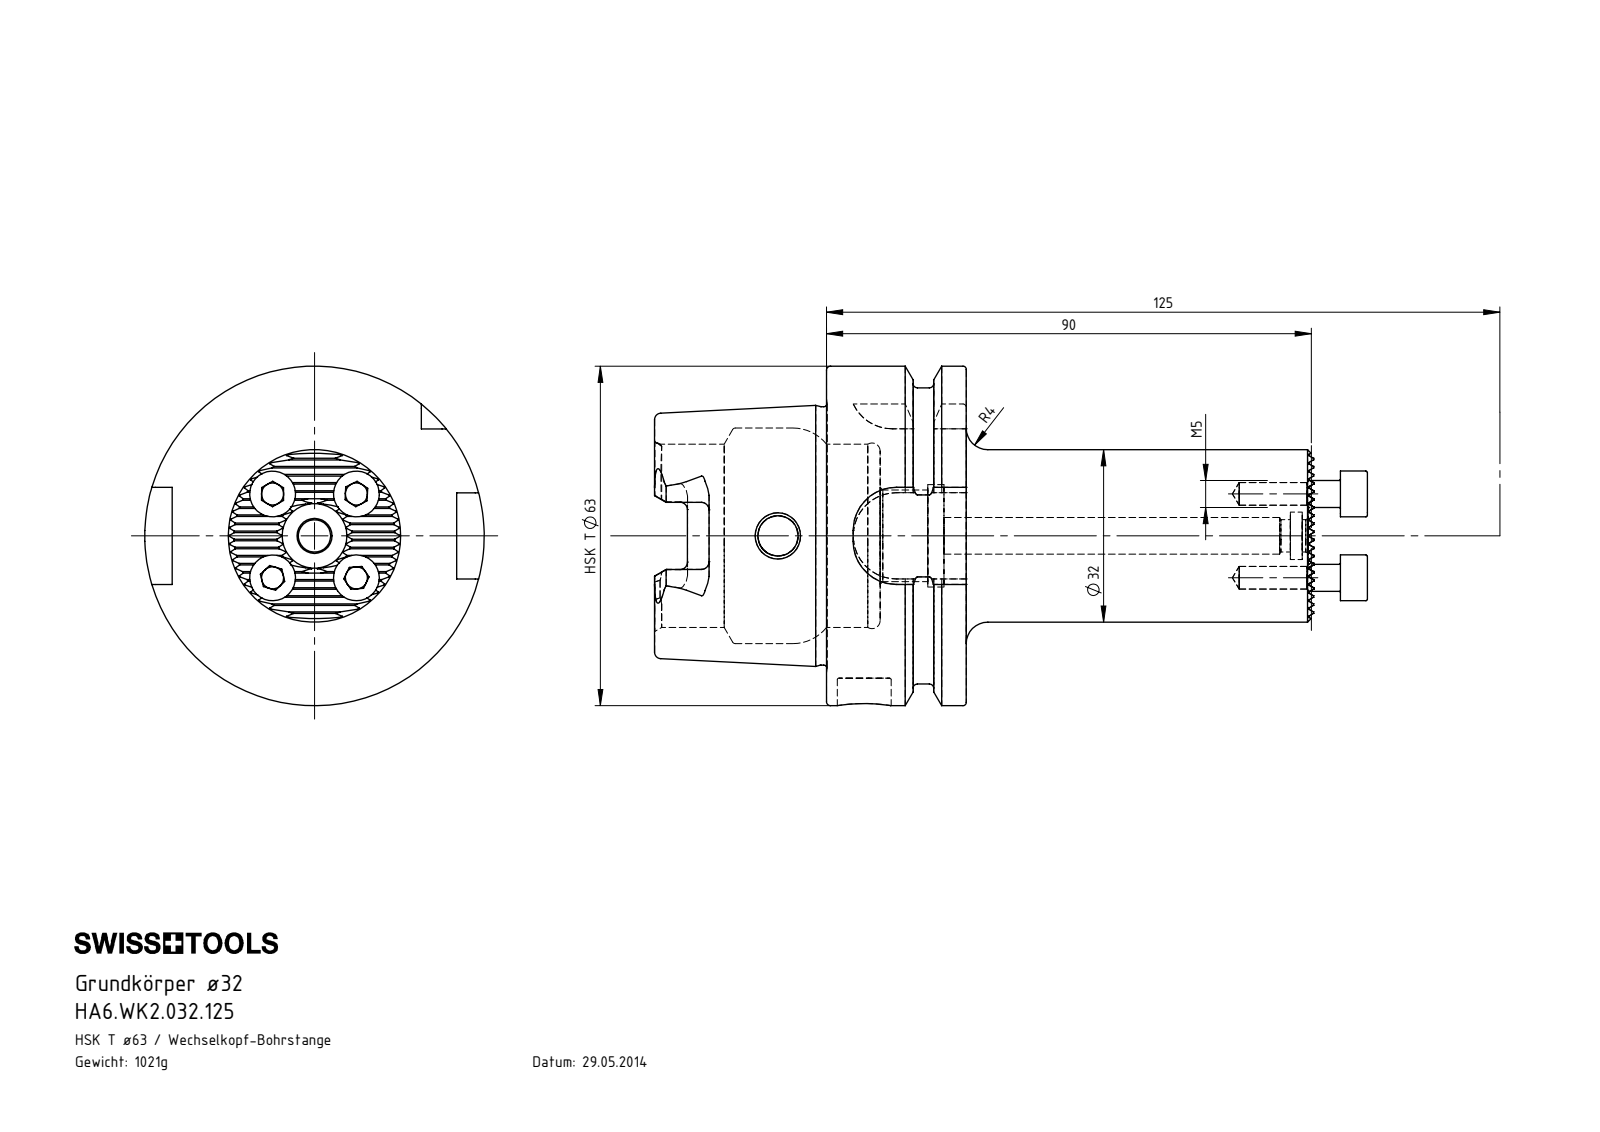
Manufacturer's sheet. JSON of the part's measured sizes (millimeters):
{"part_name": "HA6-WK2.032.125_A; HA6.WK2.032.125; ISO 4762 - M5 x 14; DIN 3771 - 6x1", "step_written_by": "SolidWorks 2017 (AUTOMOTIVE_DESIGN)", "units": "millimeters", "bodies": {"solids": 5, "faces": 386, "planar": 223, "cylindrical": 86, "other": 77}, "overall_size": [132.3, 63, 63], "volume_mm3": 131561, "surface_area_mm2": 32413, "round_holes": [[4.2, 4], [6, 1], [6.8, 1], [7.4, 1], [7.5, 1], [10, 1], [17, 1], [19, 1], [34, 1], [40, 1]], "round_bosses_or_shafts": [[8.5, 3], [5, 3], [63, 1], [54.95, 1], [47.94, 1], [32, 1]], "partial_cylinders_radius": [[0.12, 21], [1.4, 6], [2.88, 4], [8, 4]], "face_to_face_distances": [25.95, 1.3, 16, 9.95, 2.6, 3.9, 5.2, 31.9, 41.85, 57.85], "hole_center_spacings": [11, 15.56, 22.01]}
